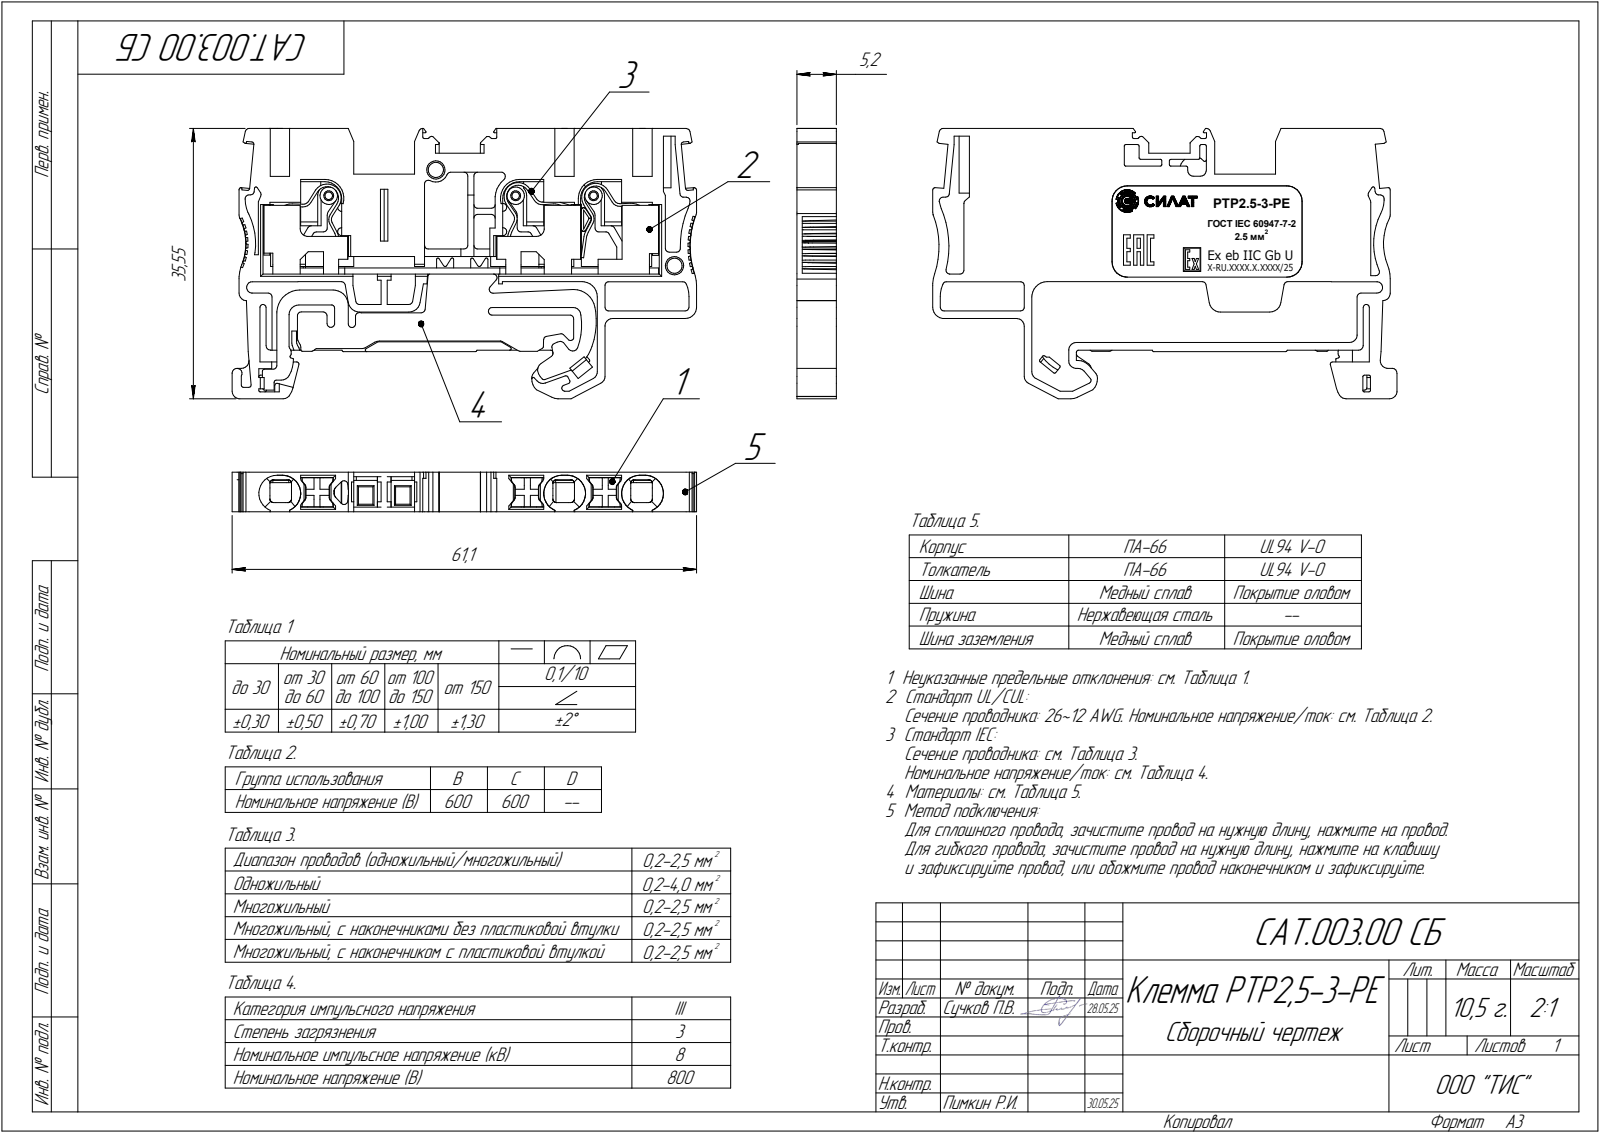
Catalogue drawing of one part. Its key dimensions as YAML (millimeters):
part_name: "Клемма PTP2,5-3-PE"
step_written_by: "SolidWorks 2024 (AUTOMOTIVE_DESIGN)"
units: millimeters
bodies: {solids: 1, faces: 388, planar: 256, cylindrical: 123, other: 9}
overall_size: [61.1, 35.55, 5.2]
volume: 8284
surface_area: 4996
partial_cylinders:
  - {radius: 0.5, count: 55}
  - {radius: 1, count: 8}
  - {radius: 0.2, count: 7}
  - {radius: 0.3, count: 7}
  - {radius: 0.15, count: 6}
  - {radius: 2.4, count: 6}
  - {radius: 5, count: 3}
  - {radius: 0.1, count: 2}
face_to_face_distances: [5.2, 29.15, 29.35, 24.51, 24.71, 4.64, 2.75, 4.15, 45.4, 12.05]
